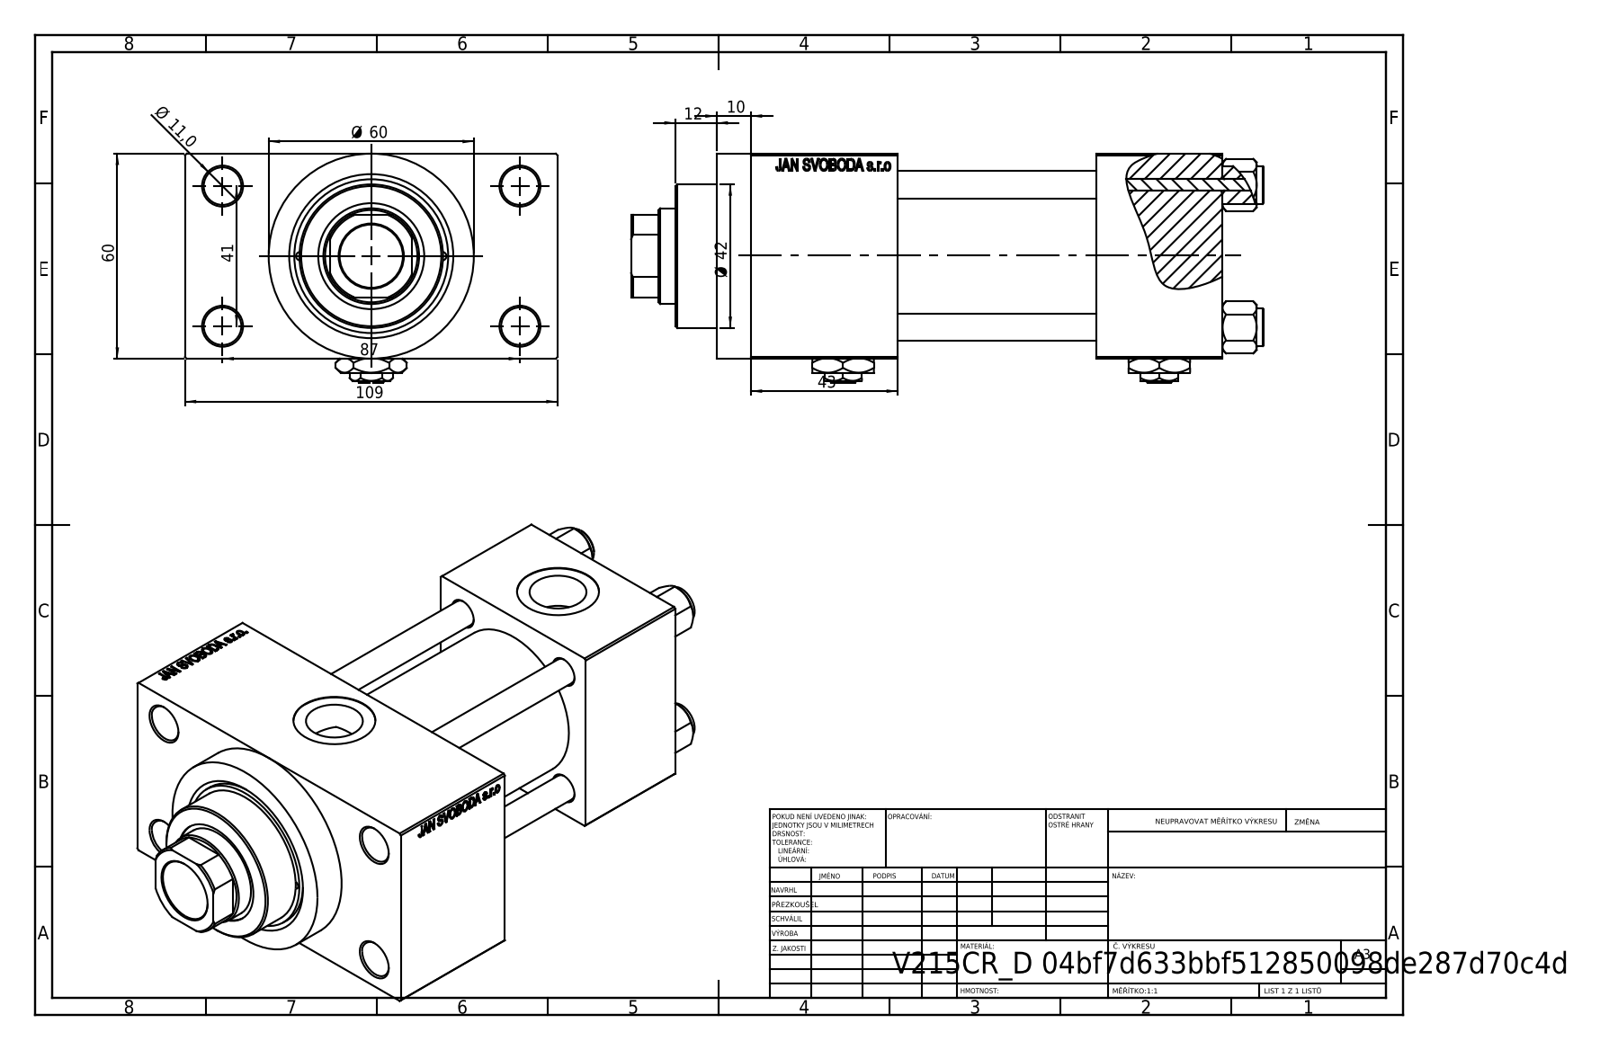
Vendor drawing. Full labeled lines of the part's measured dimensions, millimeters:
Part name (STEP PRODUCT): V215CR_VCP_D; Zatka_pro_OIL_PORT; V215_VC_A; V215CR_D_TYCINKA (+2 more)
STEP written by: SolidWorks 2019 (CONFIG_CONTROL_DESIGN)
Units: millimetres
Bodies: 13 solids, 1216 faces (550 planar, 104 cylindrical, 562 other)
Overall size (bounding box): 185 × 109 × 67
Volume: 531 735 mm³ · Surface area: 130 444 mm²
Round holes (diameter × count): ⌀8 ×4, ⌀11 ×4, ⌀2.5 ×2, ⌀7 ×2, ⌀16.66 ×2, ⌀24 ×2, ⌀18.5 ×1, ⌀28 ×1, ⌀31 ×1, ⌀40 ×1, ⌀45 ×1
Round bosses / shafts (diameter × count): ⌀11 ×4, ⌀60 ×1, ⌀46 ×1, ⌀42 ×1
Partial cylindrical surfaces — rounded edges, fillets, slot ends (radius × count): R13.5 ×1
Main face-to-face distances: 60, 84.5, 24.5, 58, 37, 95, 138, 101, 43, 109
Hole centre spacings: 20.85, 22.65, 29.49, 30.62, 41.7, 46.53, 47.15, 48.09
